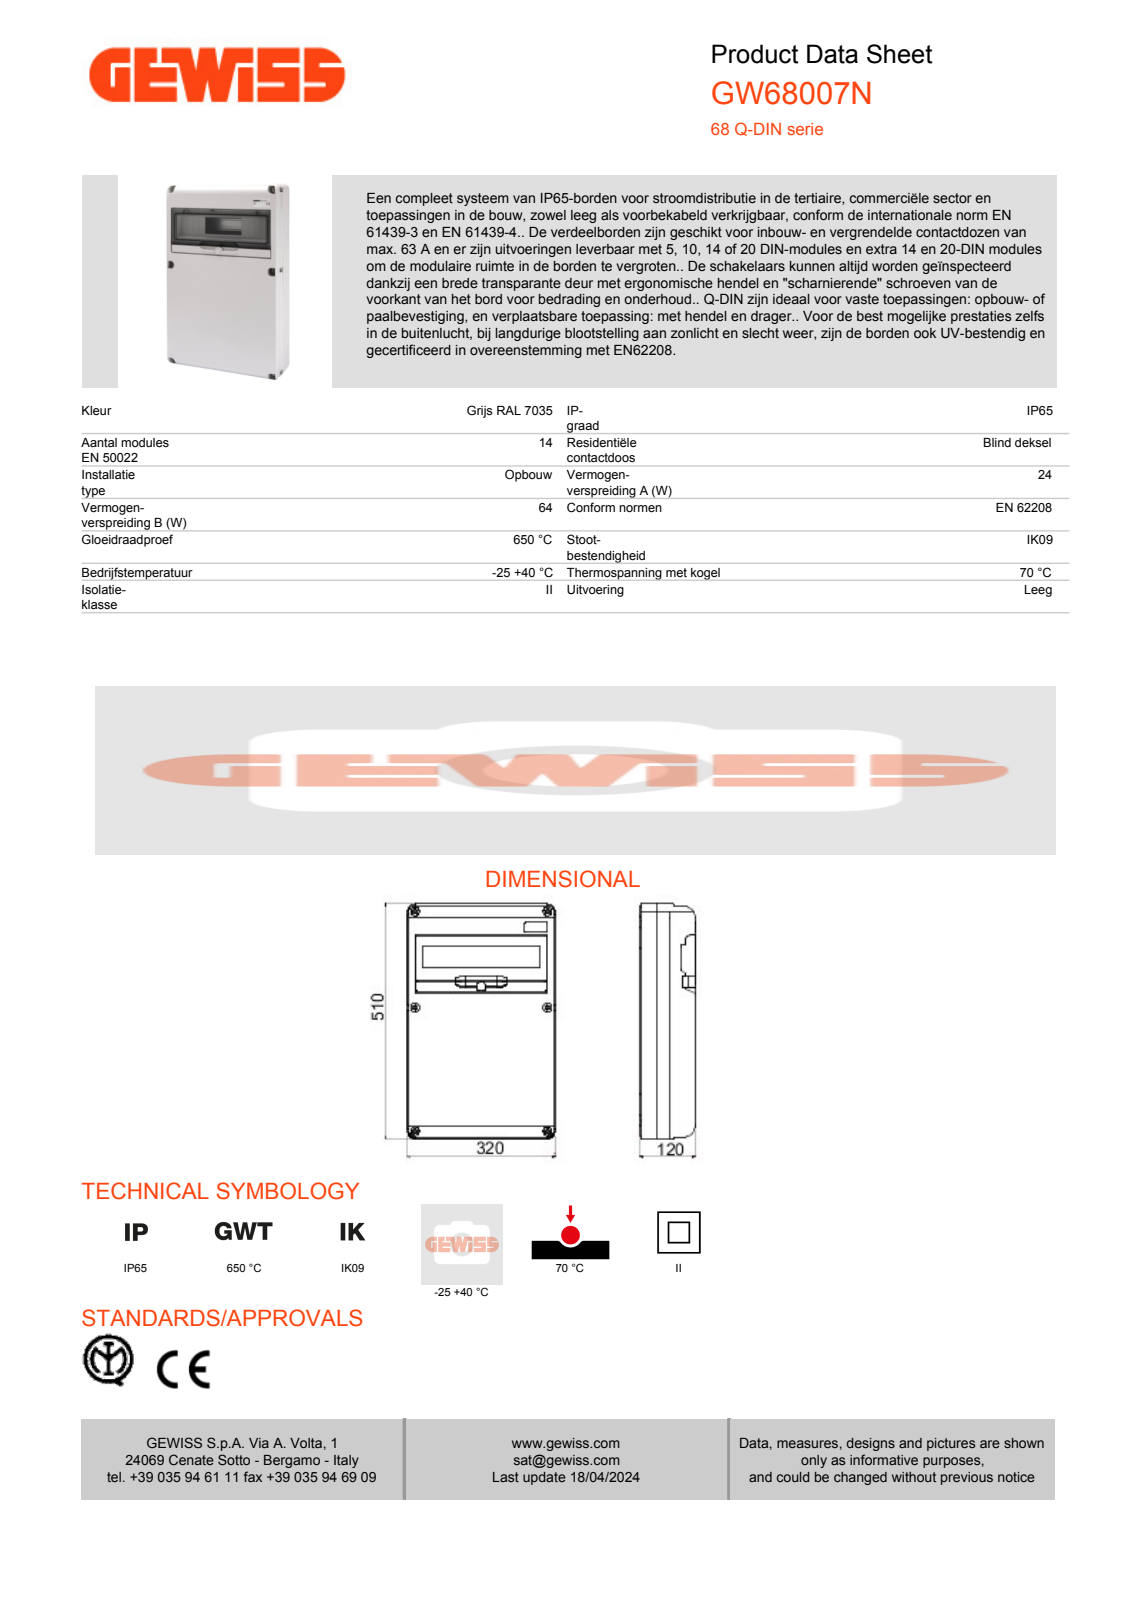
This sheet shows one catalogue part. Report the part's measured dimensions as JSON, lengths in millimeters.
{"part_name": "55523450_FONDO_14_MOD_2_GRANDEZ; 55523492F_FRON_14M_2A_GRAND_LIS; GW68007N_ASM", "step_written_by": "CREO PARAMETRIC BY PTC INC, 2020354 (CONFIG_CONTROL_DESIGN)", "units": "millimeters", "bodies": {"solids": 2, "faces": 895, "planar": 544, "cylindrical": 129, "other": 222}, "overall_size": [510.75, 321.24, 124.49], "volume_mm3": 3113000, "surface_area_mm2": 1107000, "partial_cylinders_radius": [[1.5, 25], [2, 16], [3.5, 12], [1, 8], [1.3, 8], [0.5, 6], [13, 6], [3, 4]], "face_to_face_distances": [3, 115.3, 118.3, 112.3, 320.01, 309.69, 309.62, 313.75, 4.06, 4.07]}
